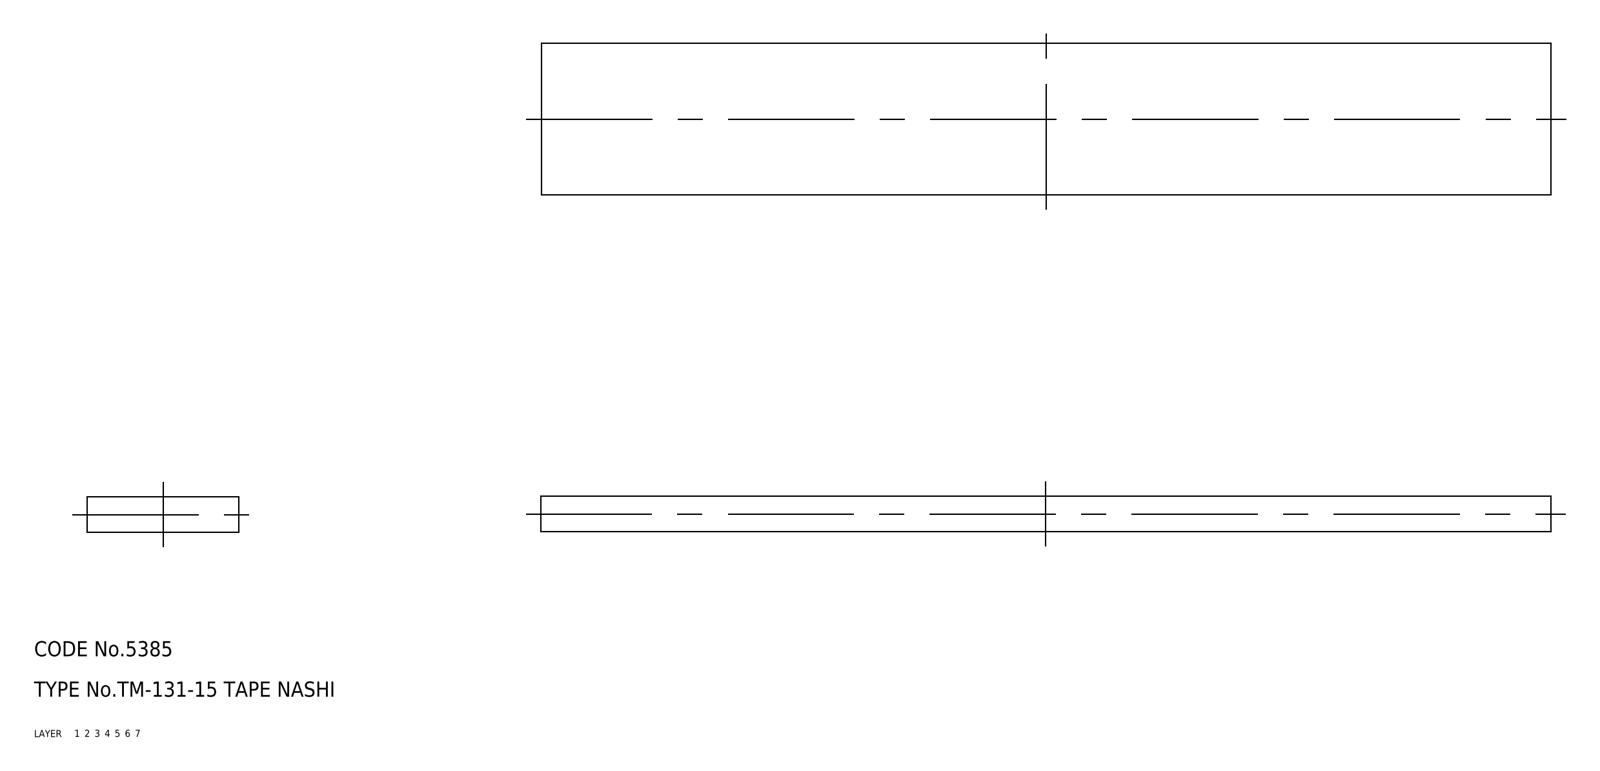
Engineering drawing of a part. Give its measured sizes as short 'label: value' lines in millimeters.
name: rubber foam
written by: CADfix (AUTOMOTIVE_DESIGN)
unit: mm
bodies: 1 solid, 6 faces (0 planar, 0 cylindrical, 6 other)
size: 200 × 30 × 7
volume: 42 000 mm³; area: 15 220 mm²
